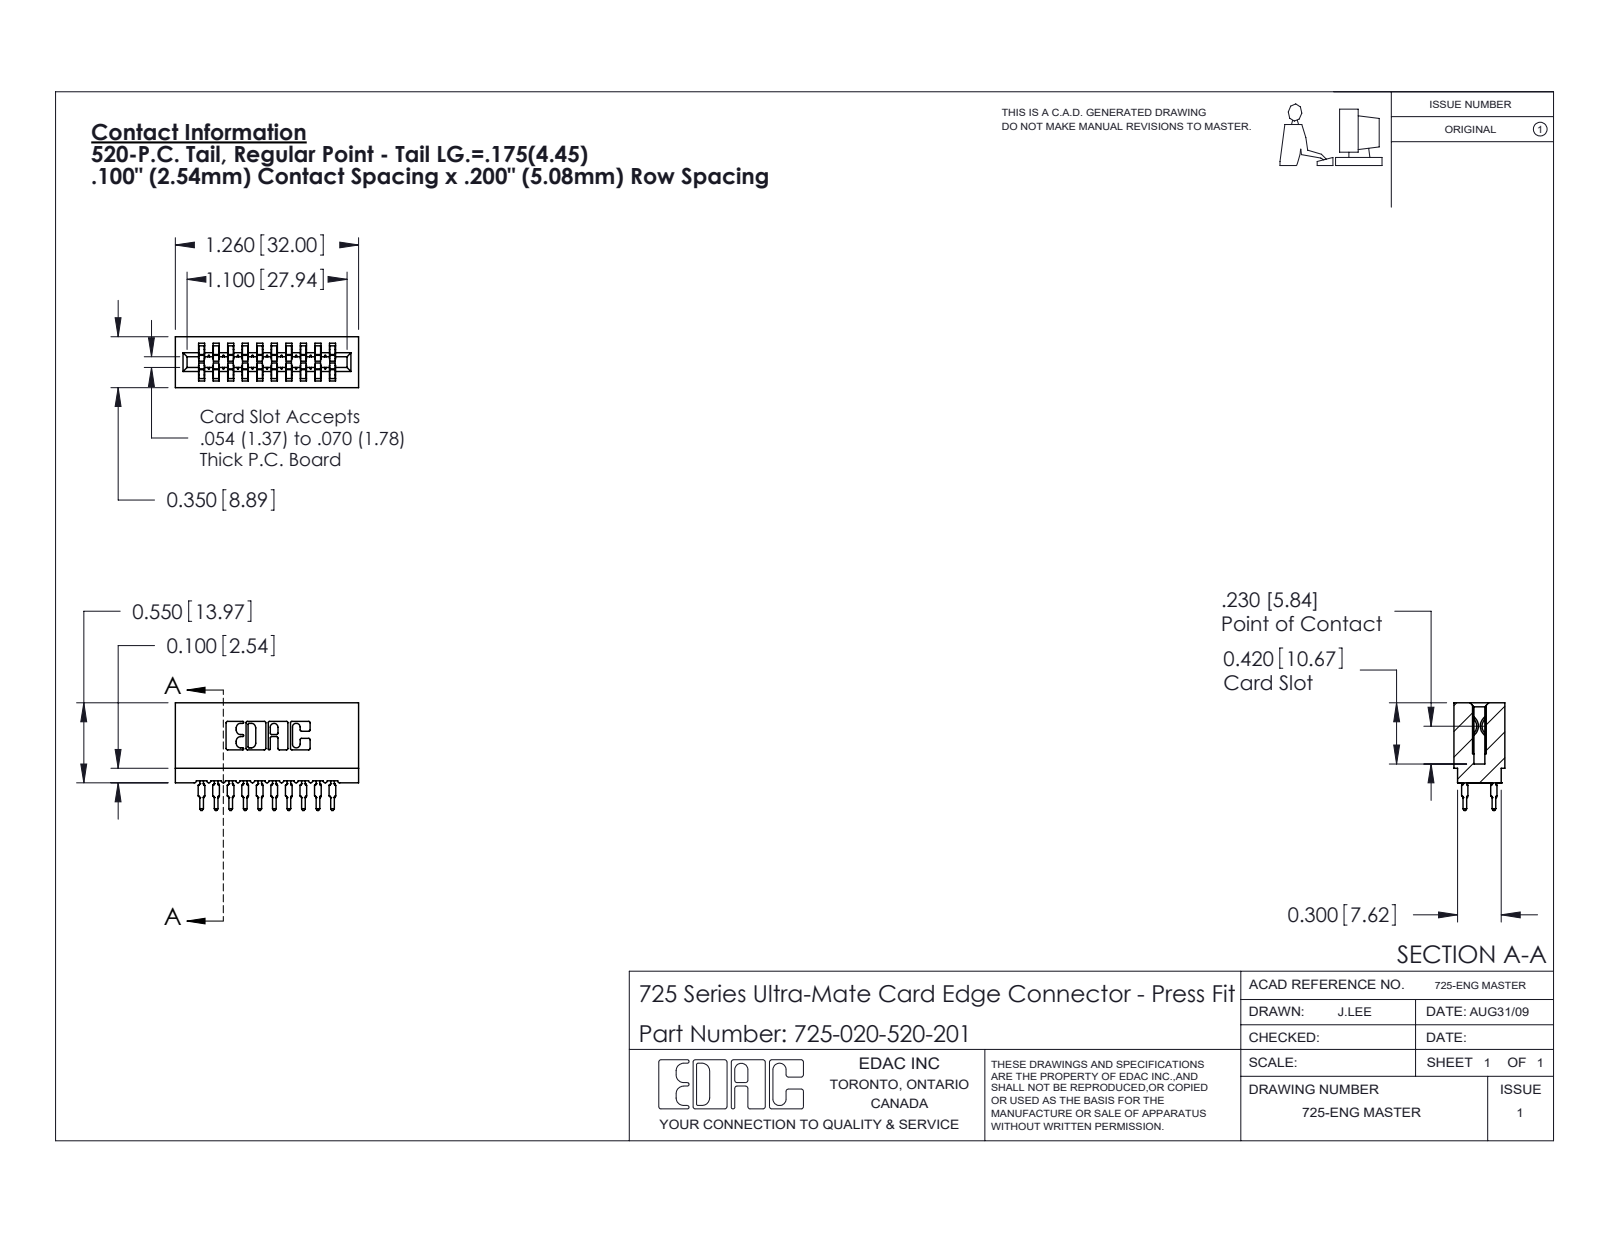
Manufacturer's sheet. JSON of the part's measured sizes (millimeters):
{"part_name": "745-292-001_520; 725-020-520-201; 725 Part_Insulator Option - 01", "step_written_by": "SolidWorks 2020 (CONFIG_CONTROL_DESIGN)", "units": "millimeters", "bodies": {"solids": 21, "faces": 1885, "planar": 975, "cylindrical": 390, "other": 520}, "overall_size": [32, 18.8, 8.9], "volume_mm3": 2690, "surface_area_mm2": 4896, "partial_cylinders_radius": [[0.5, 40], [0.3, 22], [0.4, 20], [0.1, 8], [0.3, 8], [0.2, 6], [0.8, 6], [0.7, 3]], "face_to_face_distances": [2.5, 5.1, 7.6, 10.2, 1.1, 12.7, 3.6, 1.5, 6.1, 4]}
